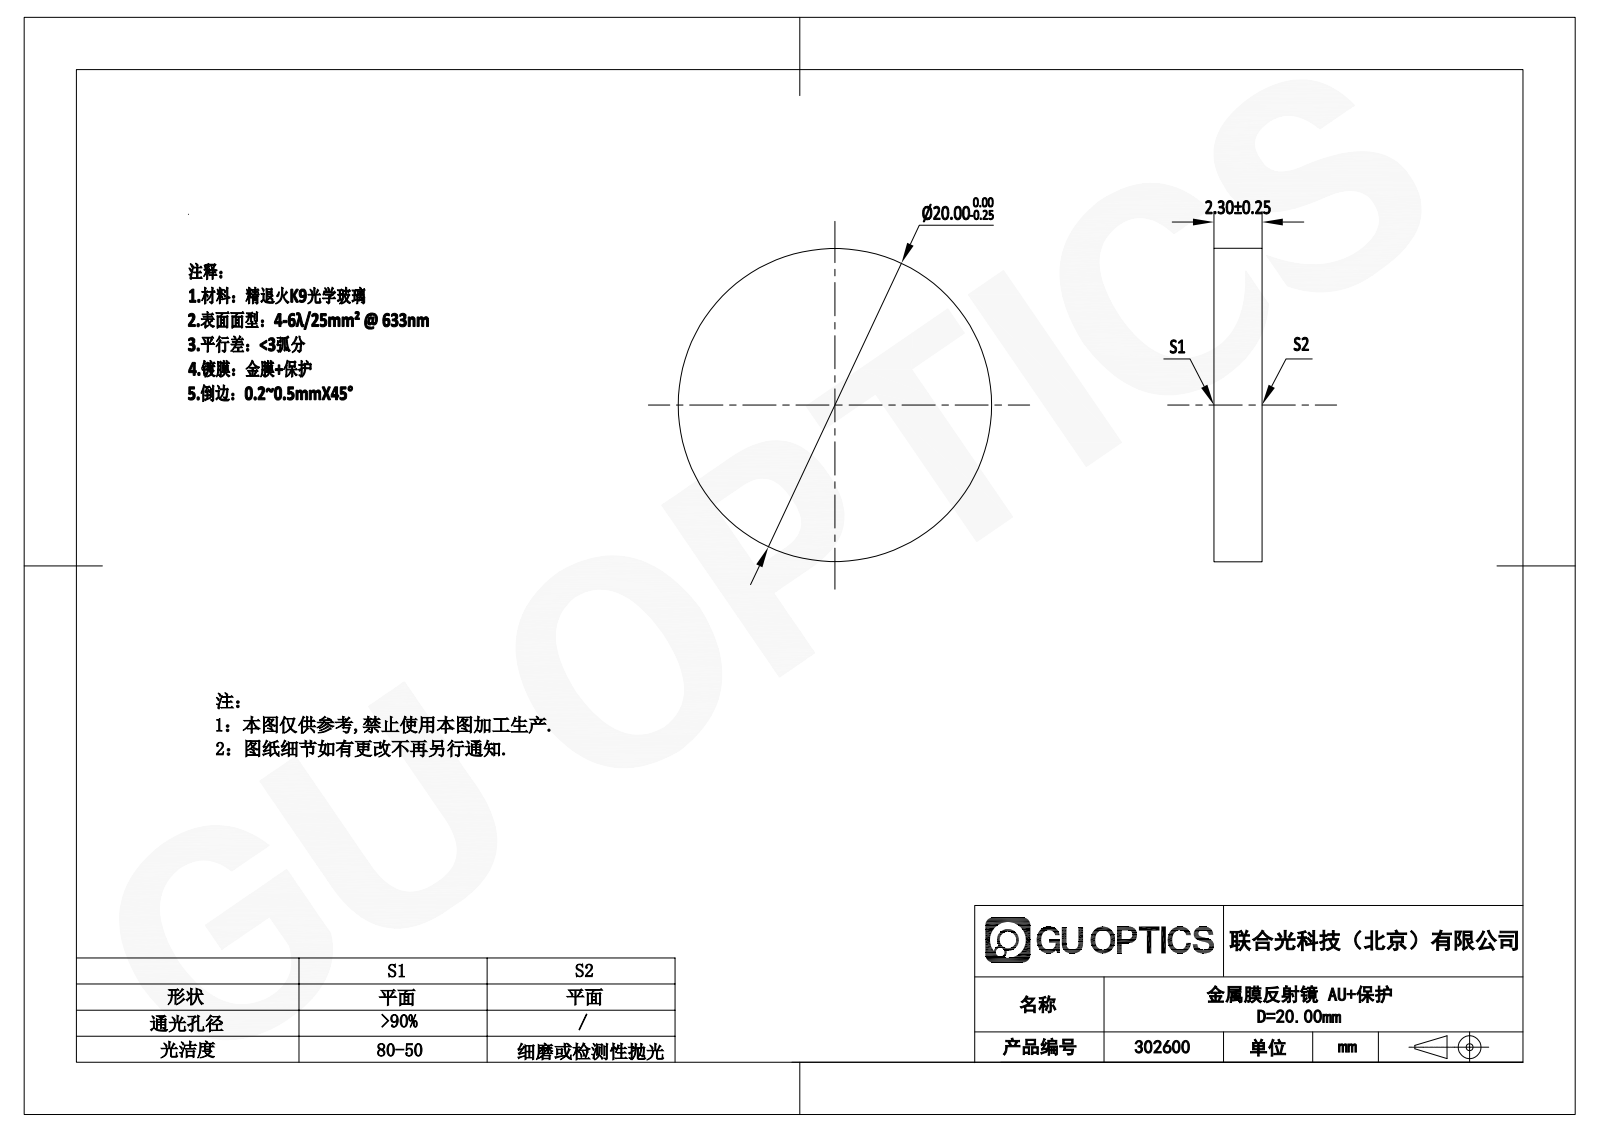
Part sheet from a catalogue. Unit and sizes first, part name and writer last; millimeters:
Units: millimetres
Overall size (bounding box): 20 × 20 × 2.3
Round bosses / shafts (diameter × count): ⌀20 ×1
Main face-to-face distances: 2.3
Volume: 723 mm³ · Surface area: 773 mm²
Bodies: 1 solid, 4 faces (2 planar, 2 cylindrical, 0 other)
Part name (STEP PRODUCT): 302513
STEP written by: SolidWorks 2016 (AUTOMOTIVE_DESIGN)
